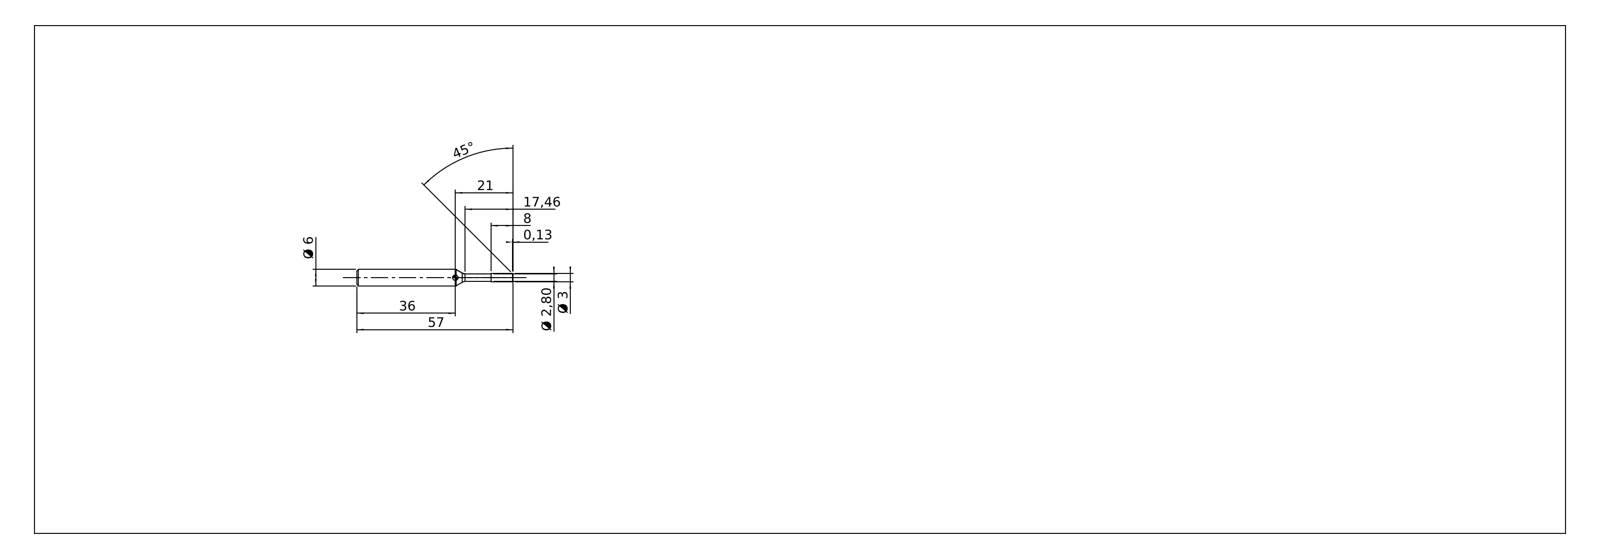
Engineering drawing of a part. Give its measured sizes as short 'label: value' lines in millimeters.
name: 733.030.99
written by: SolidWorks 2019 (CONFIG_CONTROL_DESIGN)
unit: mm
bodies: 2 solids, 11 faces (4 planar, 3 cylindrical, 4 other)
size: 57 × 6 × 6
volume: 1 183 mm³; area: 931 mm²
bosses: 1× ⌀6, 1× ⌀3, 1× ⌀2.8
face distances: 49, 8, 57
